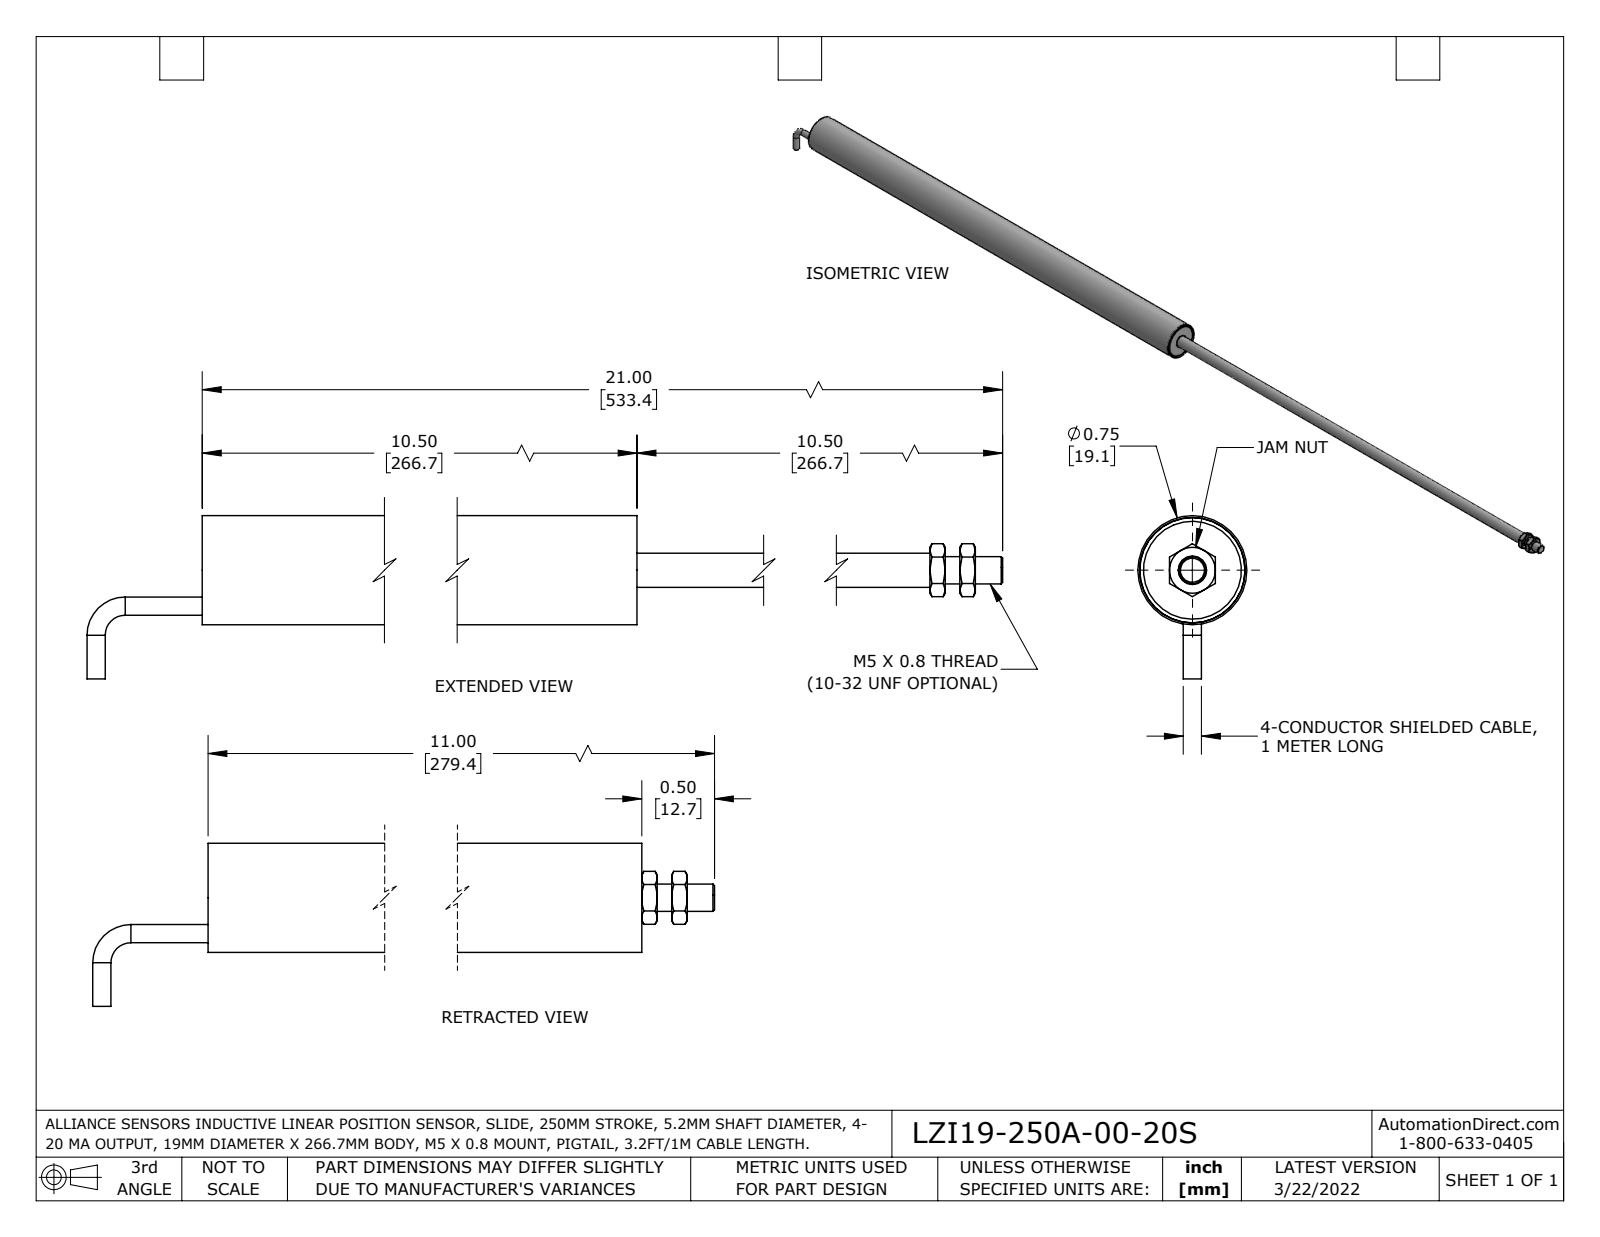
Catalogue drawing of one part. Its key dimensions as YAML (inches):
part_name: "3120-0007-ZY; 3120-0009-06_-10; 3120-0008-06_-10; 3120-0006-06_-10-0Y (+6 more)"
step_written_by: "SolidWorks 2021 (AUTOMOTIVE_DESIGN)"
units: inches
bodies: {solids: 10, faces: 137, planar: 42, cylindrical: 44, other: 51}
overall_size: [21.793, 1.121, 0.75]
volume: 1.569
surface_area: 88.58
round_holes:
  - {diameter: 0.165, count: 1}
  - {diameter: 0.188, count: 1}
  - {diameter: 0.197, count: 1}
  - {diameter: 0.234, count: 1}
  - {diameter: 0.281, count: 1}
  - {diameter: 0.68, count: 1}
  - {diameter: 0.725, count: 1}
round_bosses_or_shafts:
  - {diameter: 0.125, count: 2}
  - {diameter: 0.75, count: 1}
  - {diameter: 0.723, count: 1}
  - {diameter: 0.278, count: 1}
  - {diameter: 0.187, count: 1}
partial_cylinders:
  - {radius: 0.052, count: 1}
face_to_face_distances: [0.06, 10.42, 0.08, 10.36, 10.48, 0.315, 0.206, 0.106, 0.374, 10.5]
